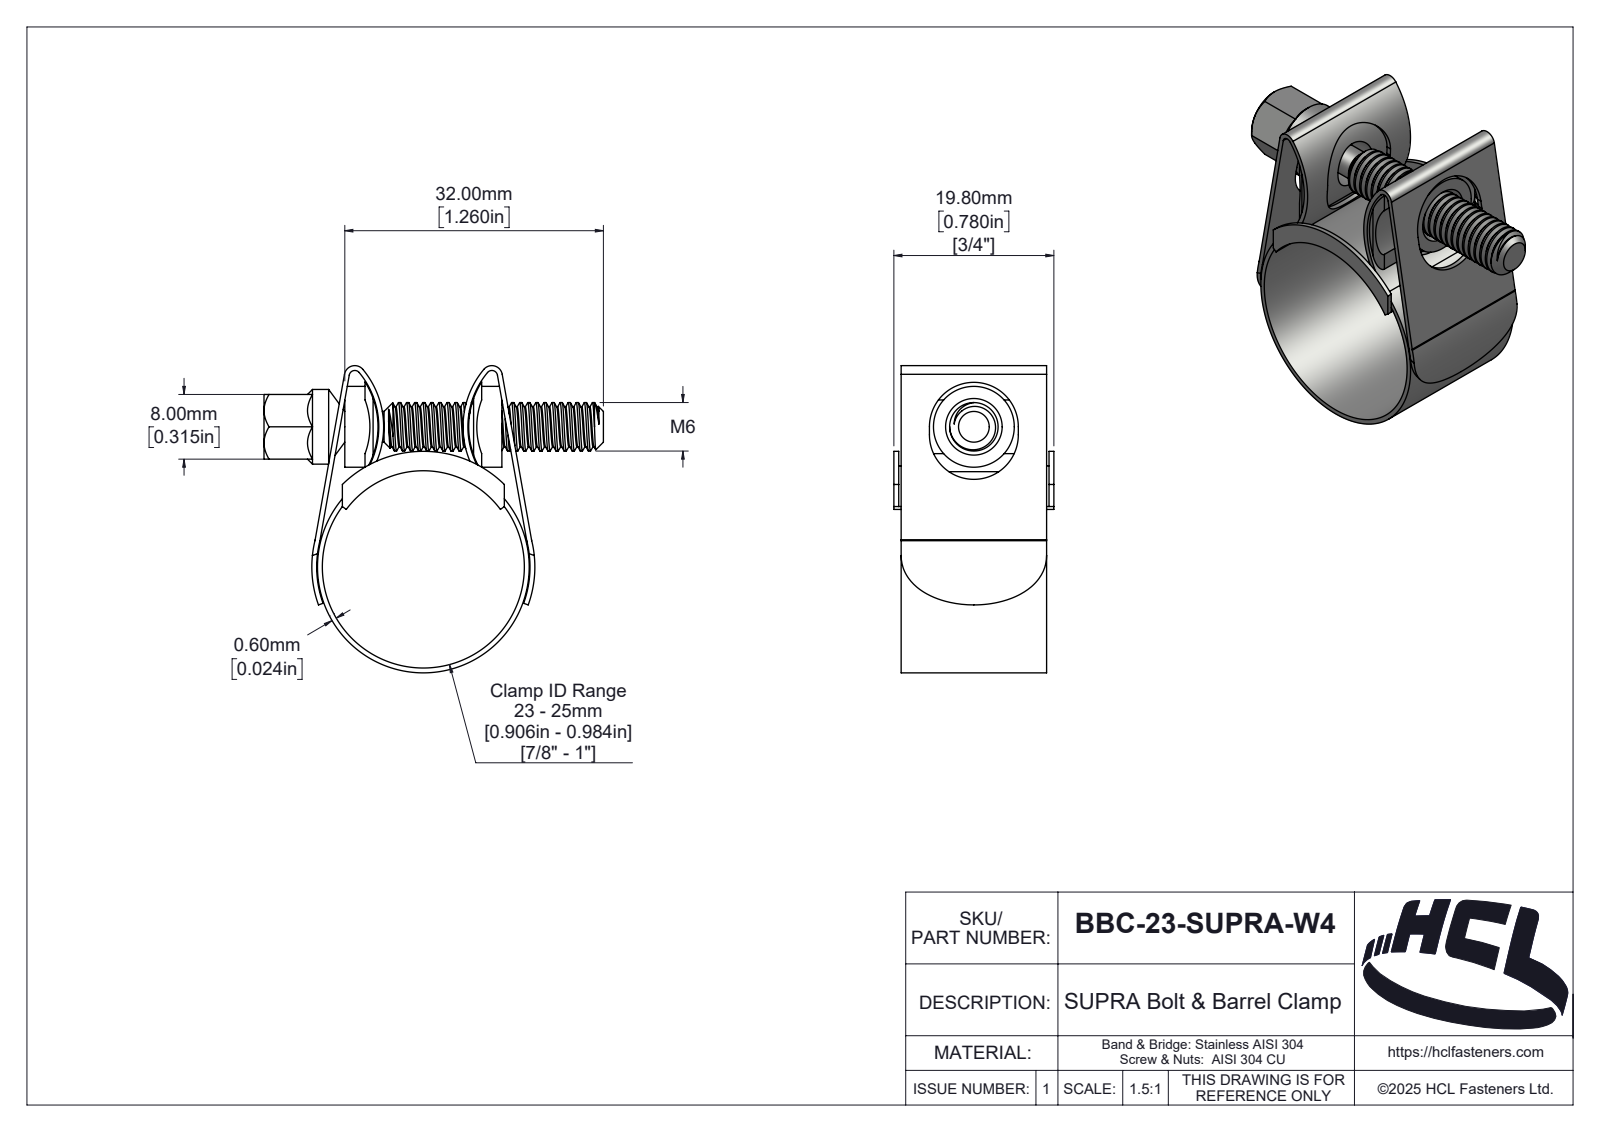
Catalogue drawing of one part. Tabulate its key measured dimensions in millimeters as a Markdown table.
| quantity | value |
| --- | --- |
| part name | BBC-23-SUPRA-W4 |
| STEP written by | SolidWorks 2025 (AUTOMOTIVE_DESIGN) |
| units | millimeters |
| bodies | 5 solids, 288 faces (44 planar, 164 cylindrical, 80 other) |
| overall size | 42 × 38 × 19.8 |
| volume | 3 483 mm³ |
| surface area | 8 261 mm² |
| round holes (diameter × count) | 25 × 1 |
| round bosses / shafts (diameter × count) | 10 × 1, 9.24 × 1, 6 × 1, 3.8 × 1 |
| partial cylindrical surfaces (radius × count) | 1 × 4, 0.7 × 2, 1.3 × 2, 2 × 2, 2.6 × 2, 5.5 × 2, 9.39 × 2, 10.39 × 2 |
| main face-to-face distances | 0.6, 0.9, 18.9, 18, 19.2, 18.3, 2.5, 16.94, 8, 19.8 |
